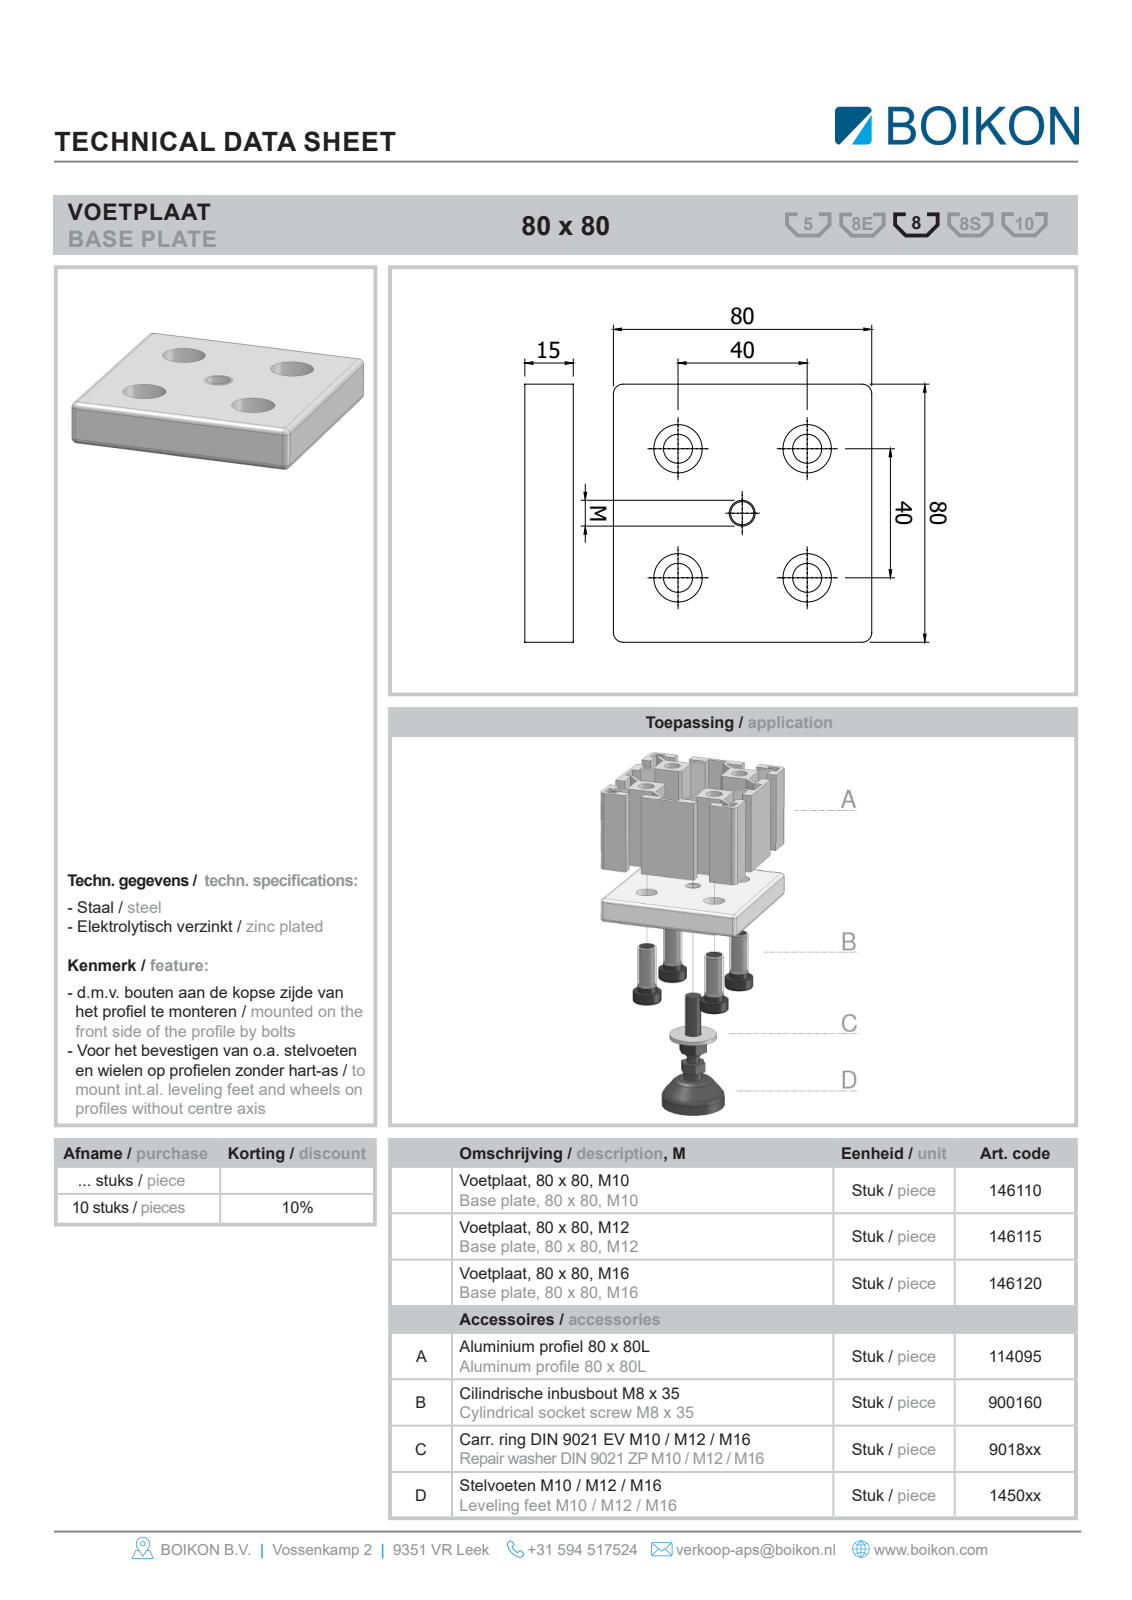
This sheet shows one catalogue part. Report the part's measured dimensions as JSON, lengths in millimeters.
{"part_name": "Root; 146120Voetplaat 80x80 M16BOIKON; 900160Cil. inbusbout DIN 912 EV M8 x 35BOIKON0", "step_written_by": "HiCAD 2013 1802.4 Build 509 (AUTOMOTIVE_DESIGN)", "units": "millimeters", "bodies": {"solids": 5, "faces": 103, "planar": 70, "cylindrical": 21, "other": 12}, "overall_size": [80, 80, 44], "volume_mm3": 93565, "surface_area_mm2": 25330, "round_holes": [[9, 4], [15, 4], [16, 1]], "round_bosses_or_shafts": [[13, 4], [8, 4], [6.47, 4]], "face_to_face_distances": [15, 80, 6, 9, 14, 8, 1, 29, 35, 43], "hole_center_spacings": [28.28, 40, 56.57]}
